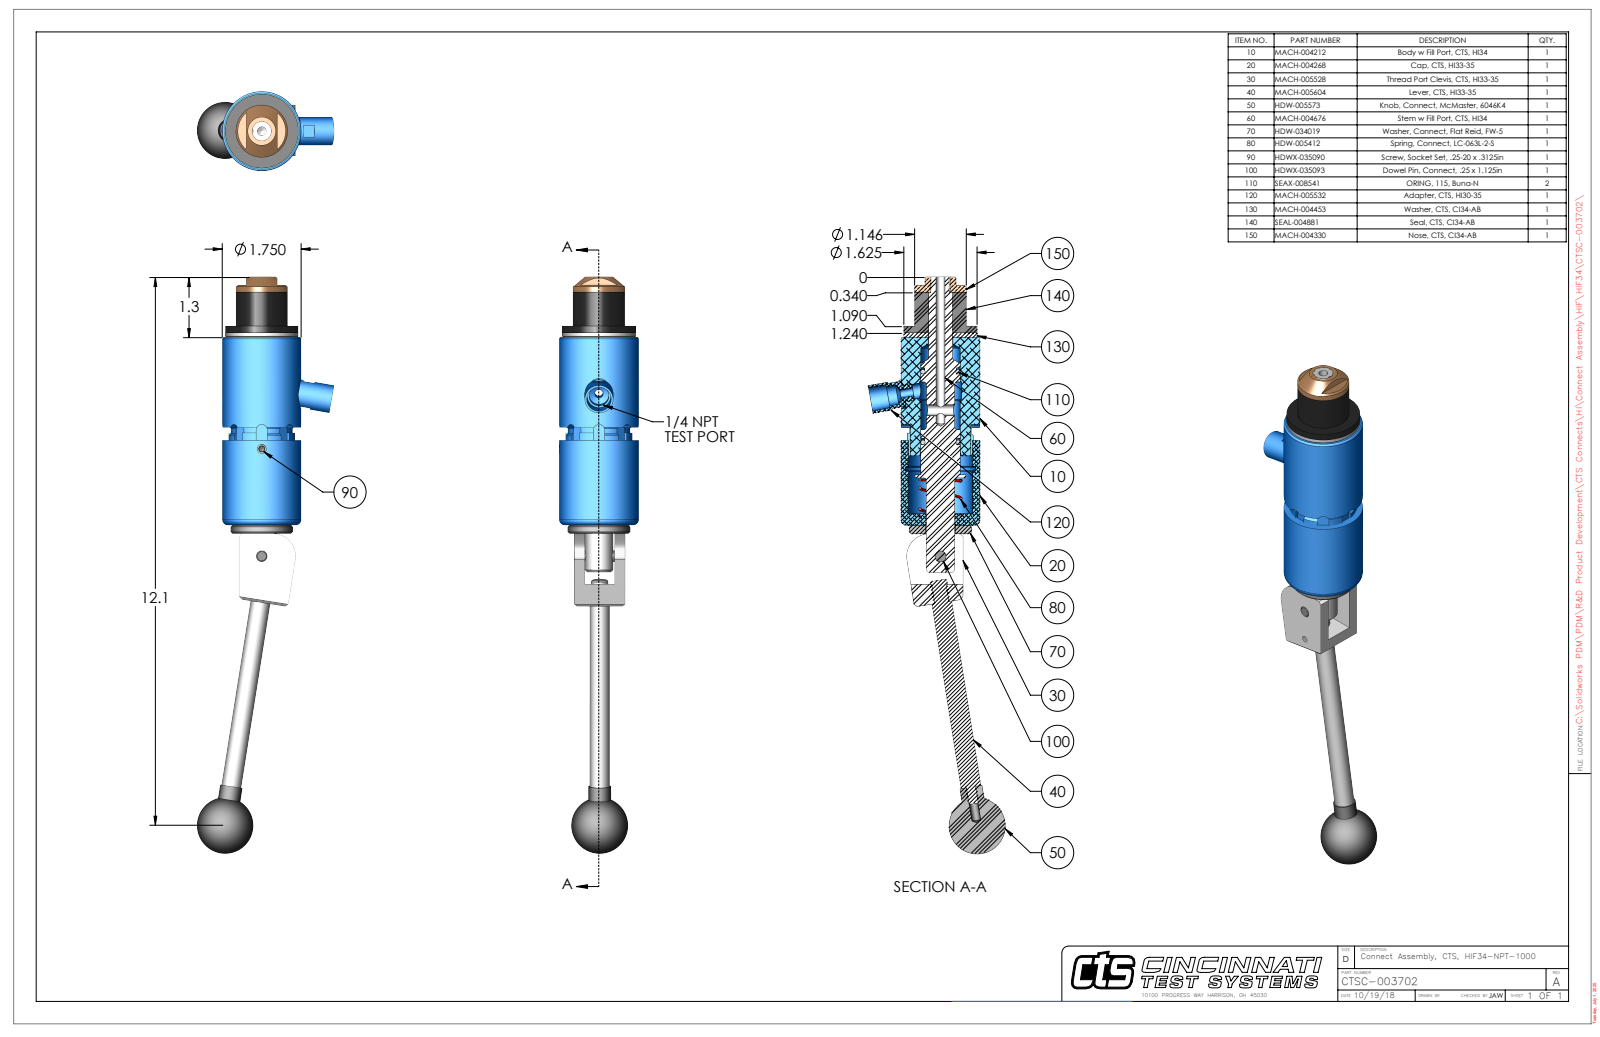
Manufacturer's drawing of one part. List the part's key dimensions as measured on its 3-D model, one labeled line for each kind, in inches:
Part name (STEP PRODUCT): CTSC-003702
STEP written by: SolidWorks 2023 (AUTOMOTIVE_DESIGN)
Units: inches
Bodies: 9 solids, 311 faces (114 planar, 133 cylindrical, 64 other)
Overall size (bounding box): 12.773 × 3.043 × 1.75
Volume: 14.6 in³ · Surface area: 83.2 in²
Round holes (diameter × count): ⌀0.201 ×2, ⌀0.15 ×1, ⌀0.187 ×1, ⌀0.204 ×1, ⌀0.249 ×1, ⌀0.25 ×1, ⌀0.251 ×1, ⌀0.313 ×1, ⌀0.422 ×1, ⌀0.438 ×1, ⌀0.53 ×1, ⌀0.541 ×1
Round bosses / shafts (diameter × count): ⌀0.5 ×2, ⌀0.44 ×2, ⌀0.25 ×2, ⌀1.75 ×1, ⌀1.625 ×1, ⌀1.38 ×1, ⌀1.146 ×1, ⌀0.625 ×1
Partial cylindrical surfaces — rounded edges, fillets, slot ends (radius × count): R0.125 ×4, R0.029 ×2, R0.166 ×1, R0.184 ×1, R0.33 ×1, R0.5 ×1, R0.695 ×1, R0.709 ×1
Main face-to-face distances: 0.094, 4.258, 4.164, 0.9, 0.994, 5.158, 1.12, 5.346, 4.446, 4.352
Hole centre spacings: 0.74, 2.376, 3.116
